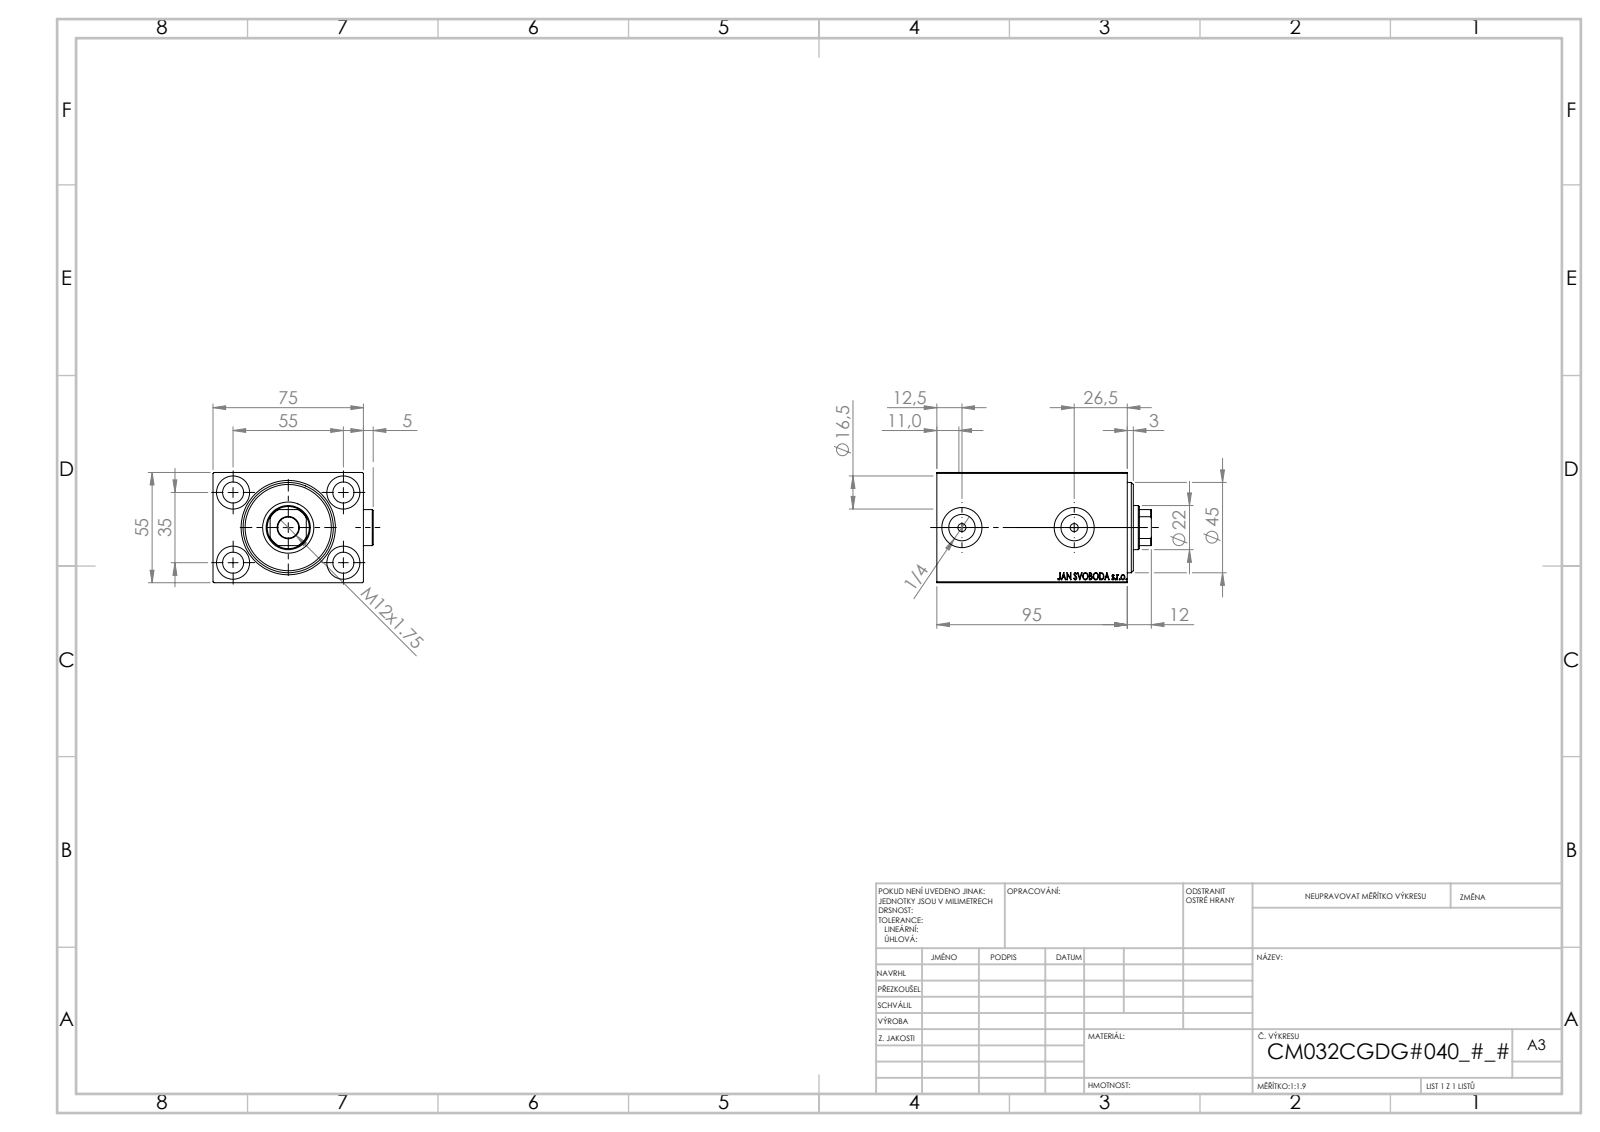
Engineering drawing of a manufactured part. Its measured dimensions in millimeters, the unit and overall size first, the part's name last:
Units: millimetres
Overall size (bounding box): 107 × 79.9 × 55
Round holes (diameter × count): ⌀10.5 ×5, ⌀16.5 ×4, ⌀4 ×2, ⌀13.16 ×2, ⌀20 ×2, ⌀22 ×1, ⌀25.5 ×1, ⌀32 ×1, ⌀34 ×1, ⌀45 ×1
Round bosses / shafts (diameter × count): ⌀18 ×2
Partial cylindrical surfaces — rounded edges, fillets, slot ends (radius × count): R10.5 ×1
Main face-to-face distances: 55, 75, 5, 10, 85, 95, 90, 80, 74.9, 73
Hole centre spacings: 32.6, 35, 55, 65.19, 56
Volume: 331 256 mm³ · Surface area: 74 498 mm²
Bodies: 5 solids, 916 faces (442 planar, 76 cylindrical, 398 other)
Part name (STEP PRODUCT): V450CM_C_VCP; V450CM_VC_B; V450CM_C_Body; Zatka_OIL_PORT
STEP written by: SolidWorks 2019 (CONFIG_CONTROL_DESIGN)
